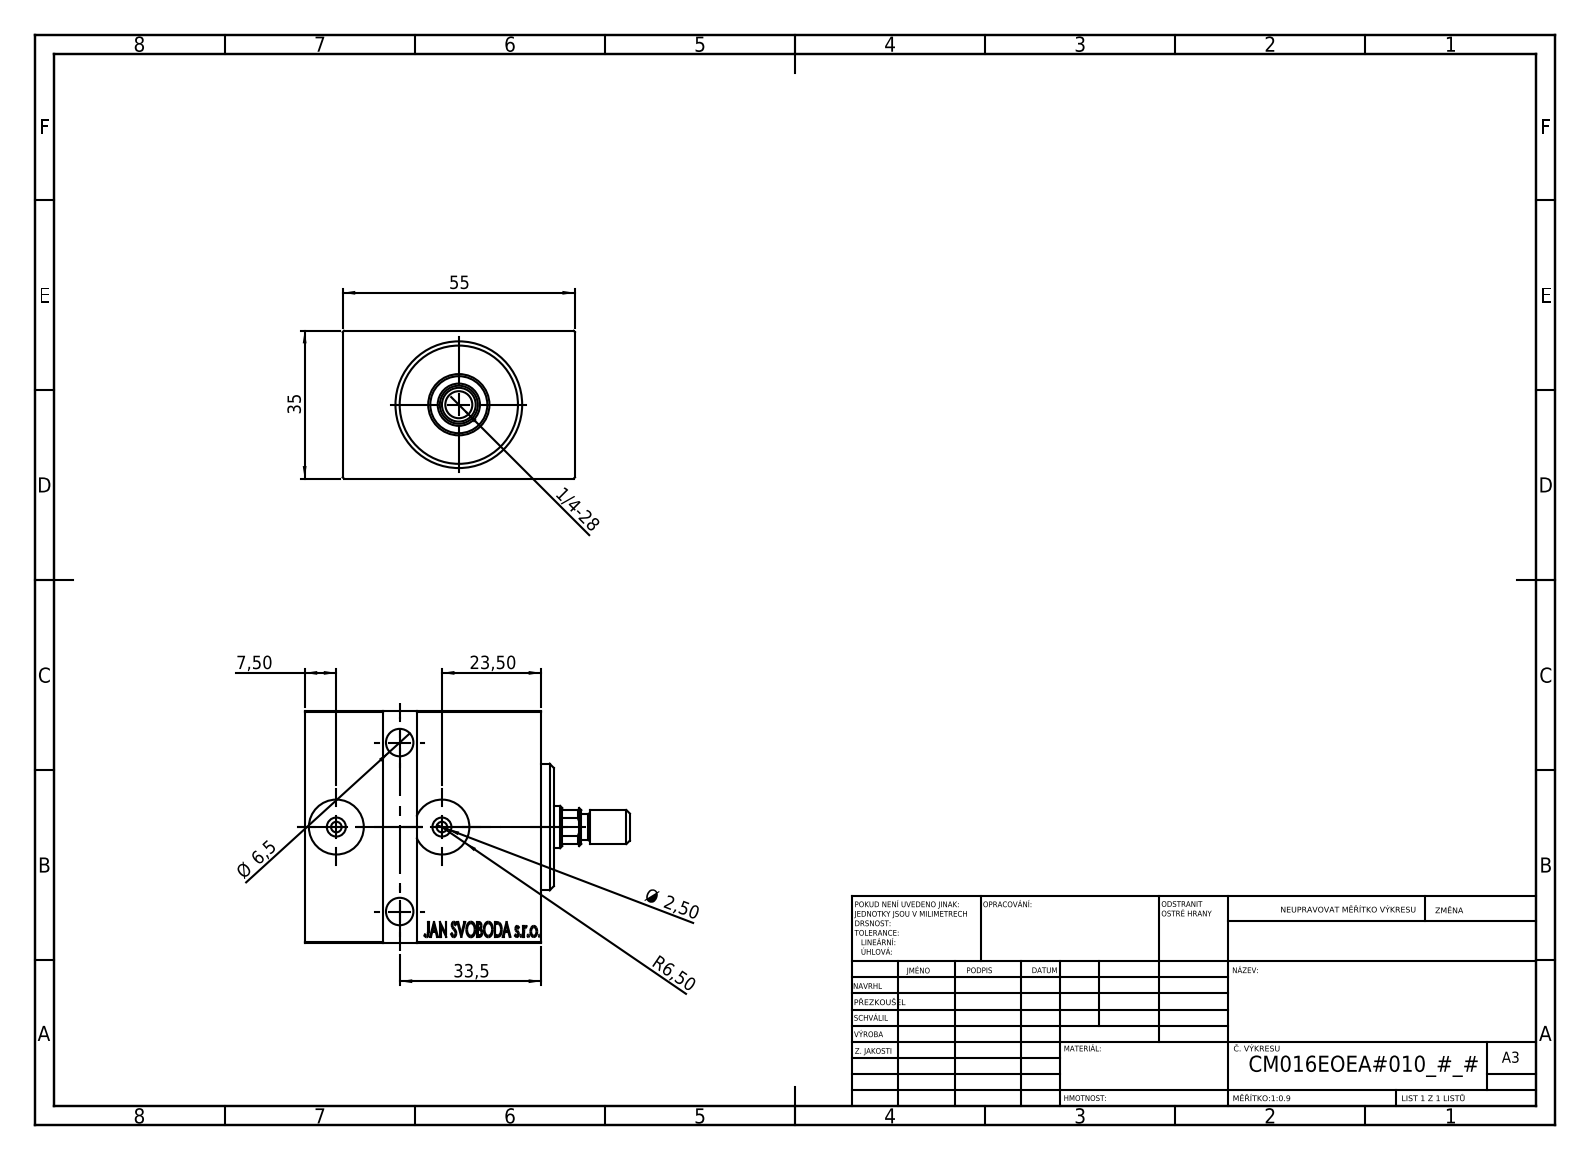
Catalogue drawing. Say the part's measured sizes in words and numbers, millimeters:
The part is named "V450CM_E_Body; V450CM_MALE_METRIC; V450CM_E_VCP; V450CM_VC_B". Its 3-D file was written by "SolidWorks 2019 (CONFIG_CONTROL_DESIGN)". It is 4 solids with 866 faces: 415 planar, 51 cylindrical and 400 other. Overall it measures 77 by 55 by 35 millimeters. Its volume is 106 299 cubic millimeters and its surface area 25 035 square millimeters. Round holes: 2 of diameter 2.5, 2 of diameter 6.5, 2 of diameter 10.5, 2 of diameter 13, 1 of diameter 4.5, 1 of diameter 10, 1 of diameter 13.5, 1 of diameter 14.5, 1 of diameter 16, 1 of diameter 25. Round bosses or shafts: 2 of diameter 4.5, 1 of diameter 30, 1 of diameter 18, 1 of diameter 8, 1 of diameter 6. Partial cylindrical surfaces (rounded edges, fillets, slot ends): 1 of radius 4.5. The main face-to-face distances are 35, 55, 56, 5, 51, 8, 3, 1, 59, 46. The hole center spacings are 25, 22.36, 40.
